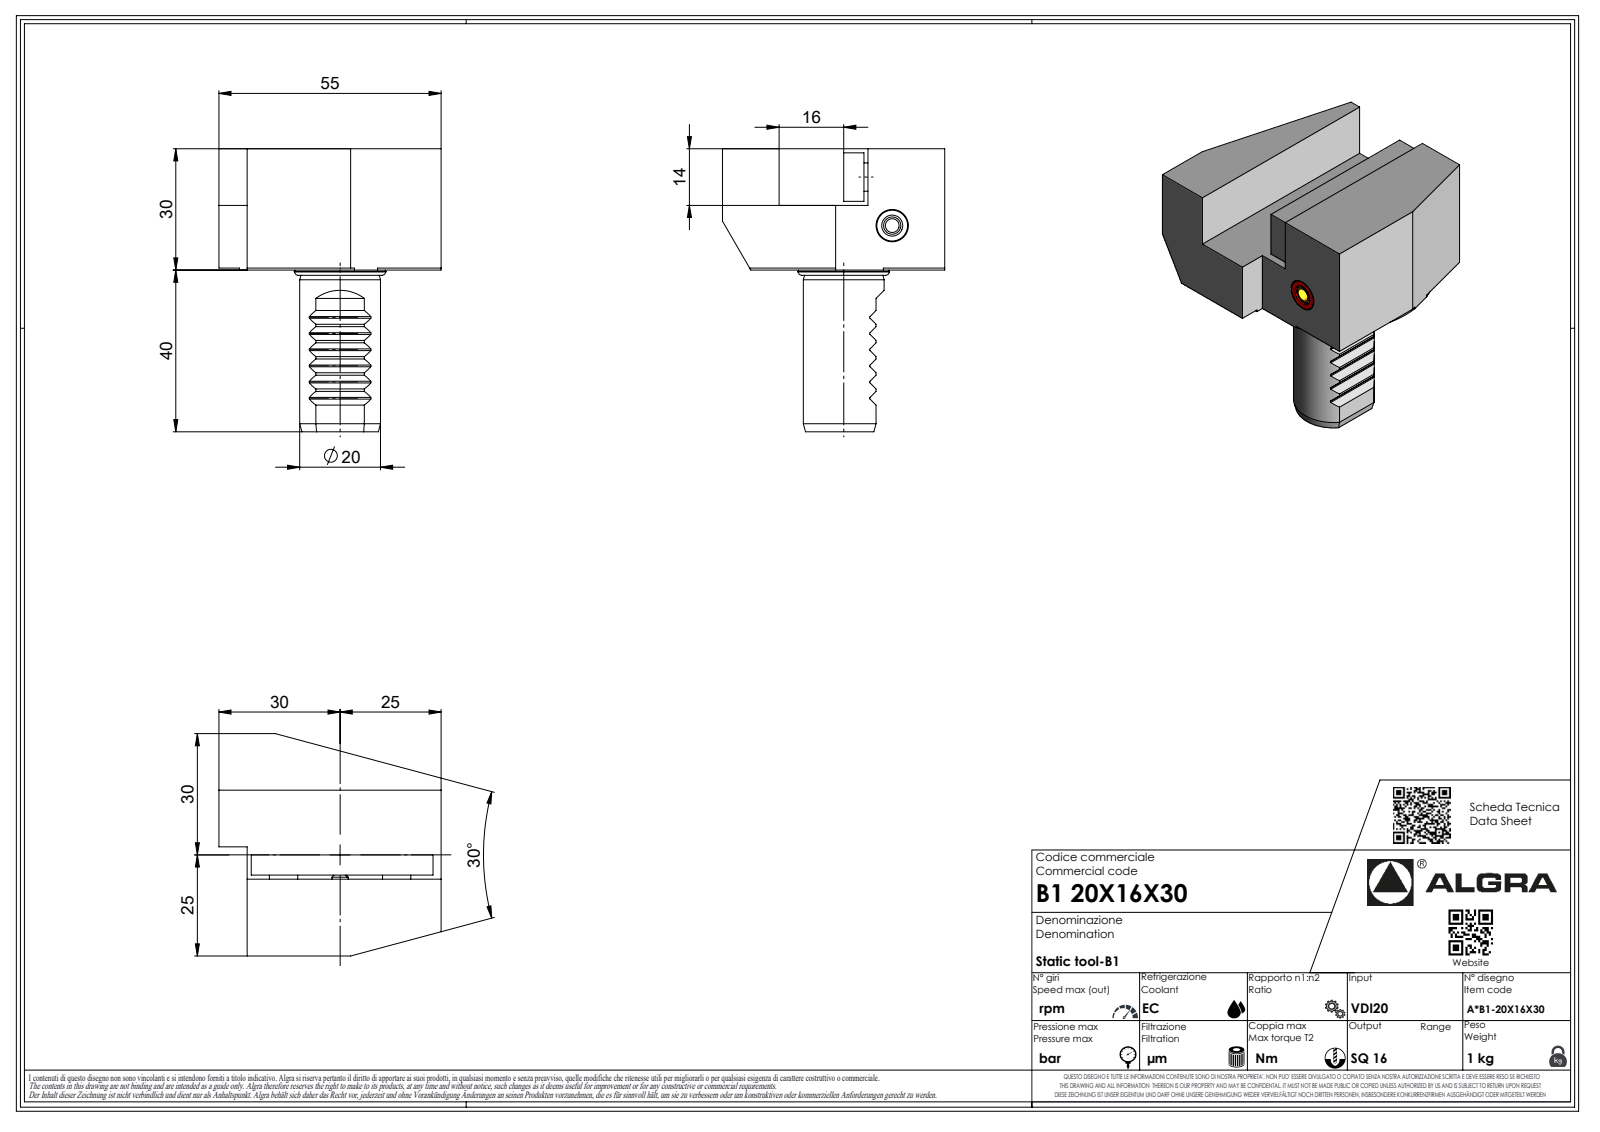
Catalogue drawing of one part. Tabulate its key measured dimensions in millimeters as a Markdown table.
| quantity | value |
| --- | --- |
| part name | B120X16X30 |
| STEP written by | SolidWorks 2023 (AUTOMOTIVE_DESIGN) |
| units | millimeters |
| bodies | 1 solid, 316 faces (209 planar, 40 cylindrical, 67 other) |
| overall size | 70 × 55 × 55 |
| volume | 73 549 mm³ |
| surface area | 16 016 mm² |
| round holes (diameter × count) | 2.1 × 1 |
| round bosses / shafts (diameter × count) | 7 × 2, 22.72 × 1, 20 × 1, 6.37 × 1, 4 × 1, 1.7 × 1 |
| partial cylindrical surfaces (radius × count) | 0.33 × 7, 0.52 × 7, 3.7 × 7, 0.3 × 6, 0.21 × 1, 25 × 1 |
| main face-to-face distances | 16, 30, 14, 1, 55, 41, 7, 48, 22, 19 |
